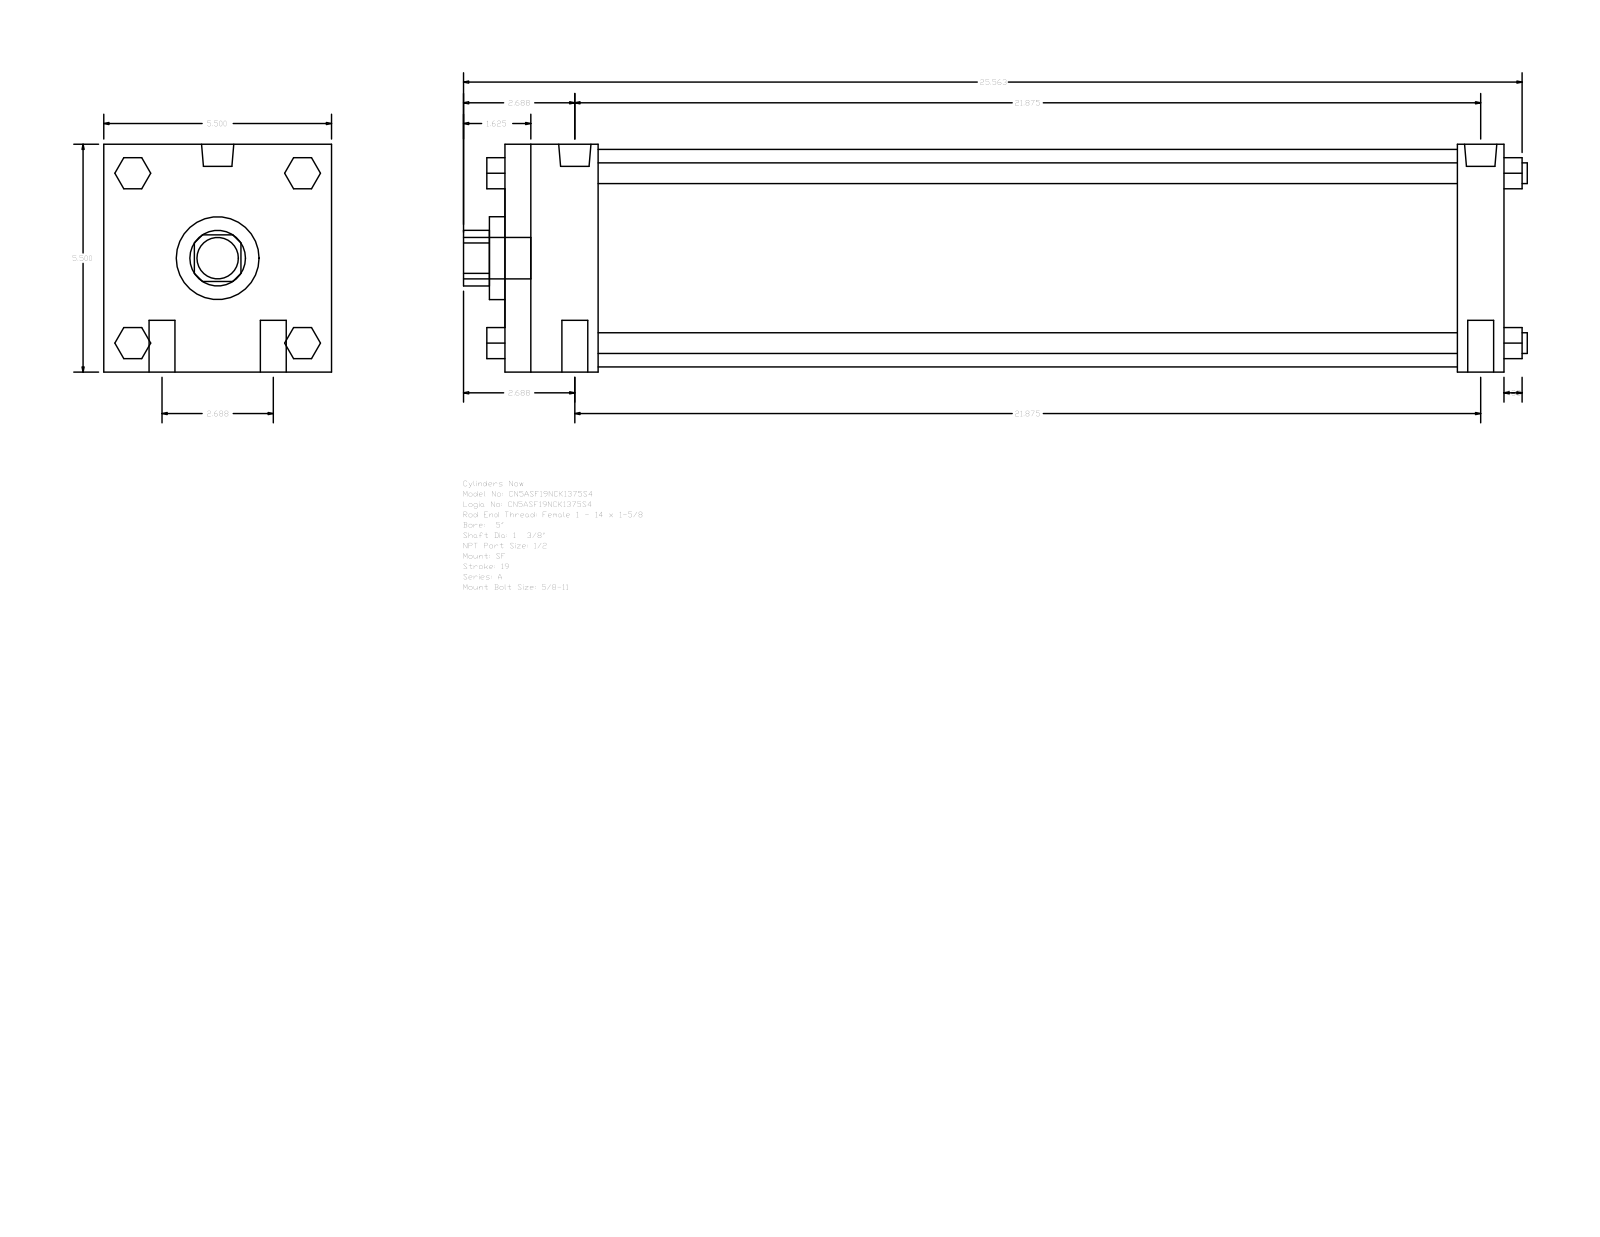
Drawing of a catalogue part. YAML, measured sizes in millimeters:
part_name: "A_SF__0500_1.375"
step_written_by: "GSSL Pune (CONFIG_CONTROL_DESIGN)"
units: millimeters
bodies: {solids: 0, faces: 124, planar: 94, cylindrical: 30, other: 0}
overall_size: [652.46, 139.7, 139.7]
round_holes:
  - {diameter: 34.92, count: 1}
  - {diameter: 50.8, count: 1}
  - {diameter: 133.35, count: 1}
round_bosses_or_shafts:
  - {diameter: 15.88, count: 4}
  - {diameter: 12.7, count: 4}
  - {diameter: 19.77, count: 2}
  - {diameter: 8.73, count: 2}
  - {diameter: 25.4, count: 1}
partial_cylinders:
  - {radius: 17.06, count: 1}
face_to_face_distances: [139.7, 612.77, 28.57, 57.15, 584.2, 527.05, 555.62, 19.05, 52.07, 90.18]
